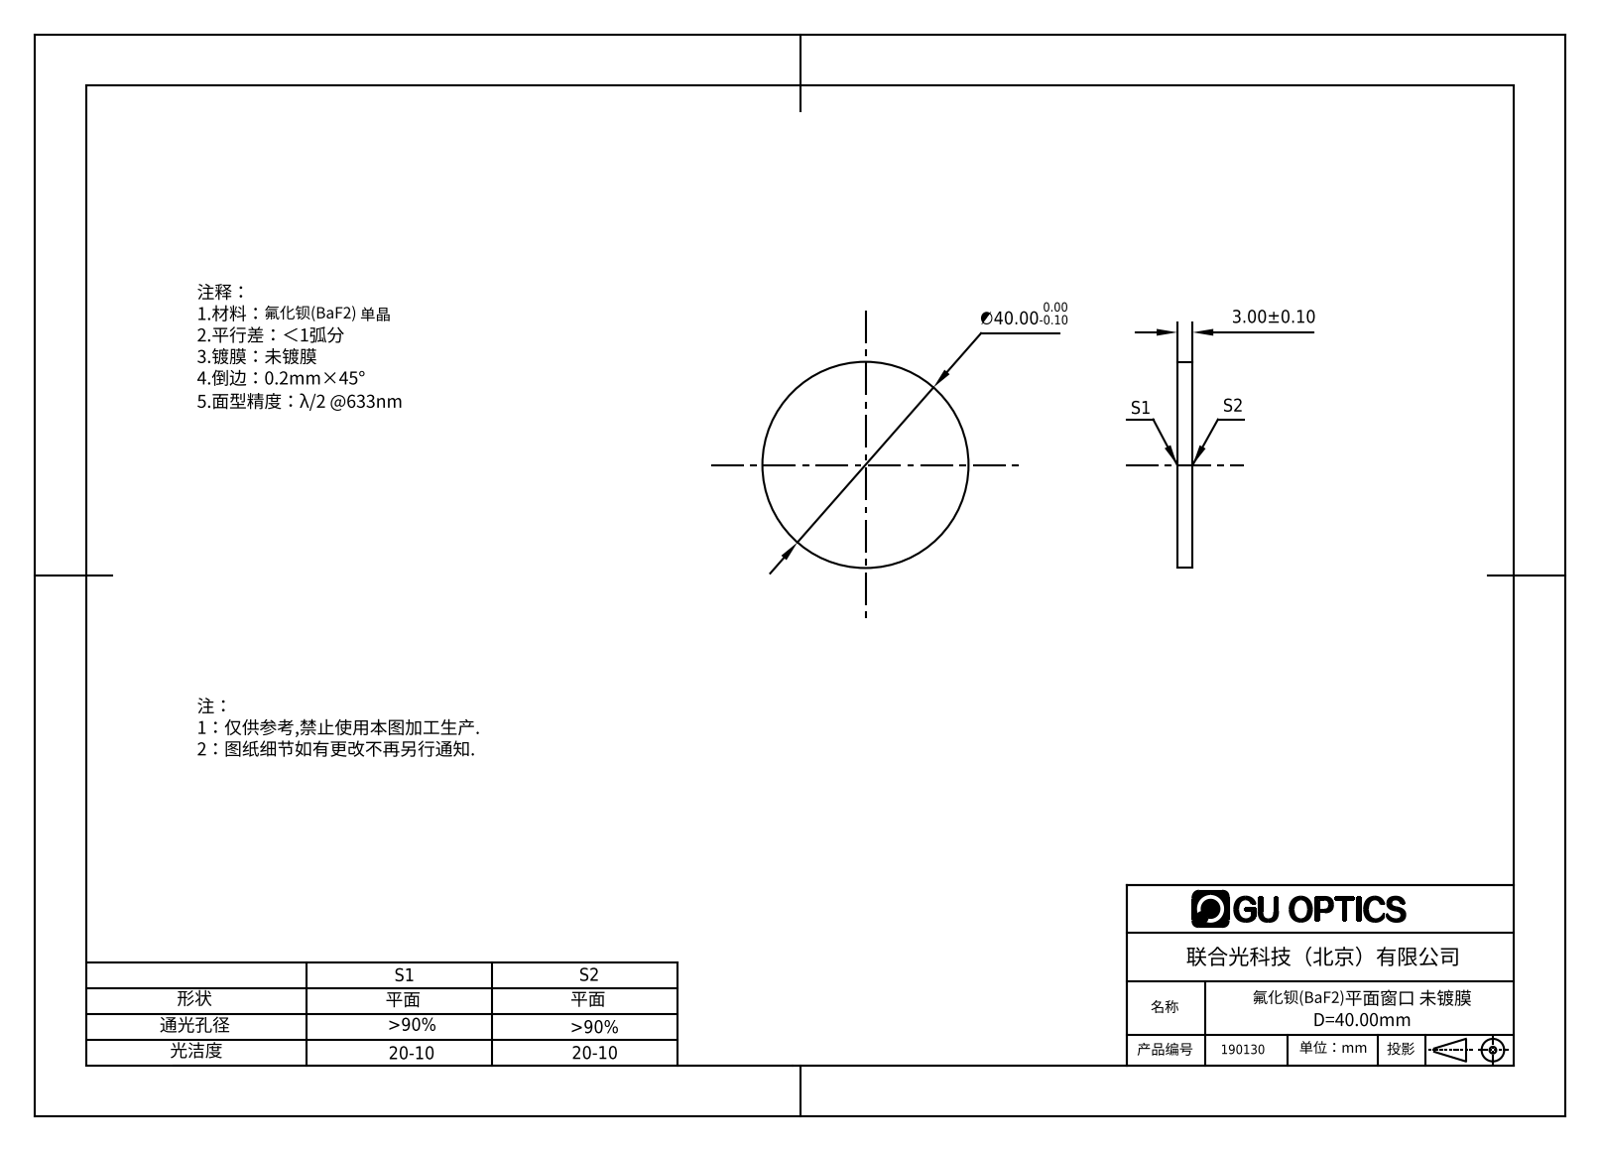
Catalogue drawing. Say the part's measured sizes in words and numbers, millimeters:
The part is named "190130". Its 3-D file was written by "SolidWorks 2016 (AUTOMOTIVE_DESIGN)". It is 1 solid with 4 faces: 2 planar, 2 cylindrical and 0 other. Overall it measures 40 by 40 by 3 millimeters. Its volume is 3 770 cubic millimeters and its surface area 2 890 square millimeters. Round bosses or shafts: 1 of diameter 40. The main face-to-face distances are 3.
